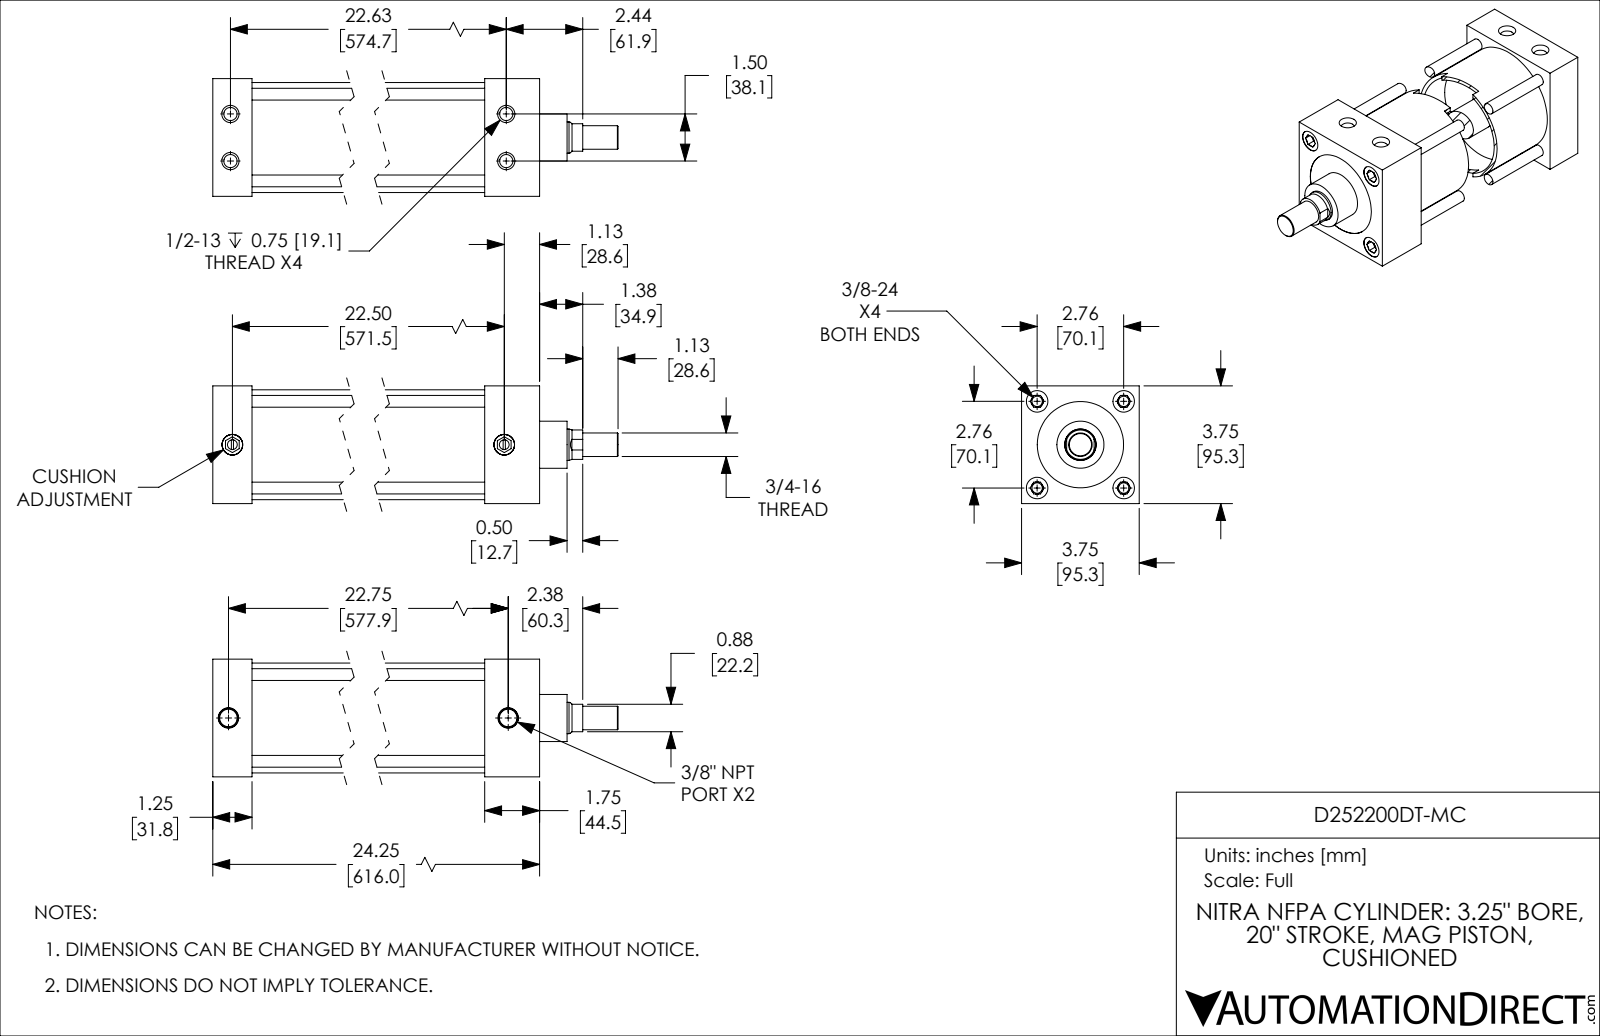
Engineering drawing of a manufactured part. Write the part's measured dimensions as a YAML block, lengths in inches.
part_name: "D252200DT-MC_CUSHION; D252200DT-MC_PISTON_KK1; D252200DT-MC_BODY; D252200DT-MC"
step_written_by: "SolidWorks 2019 (CONFIG_CONTROL_DESIGN)"
units: inches
bodies: {solids: 4, faces: 246, planar: 90, cylindrical: 78, other: 78}
overall_size: [26.75, 3.75, 3.75]
volume: 105.8
surface_area: 787
round_holes:
  - {diameter: 0.332, count: 4}
  - {diameter: 0.422, count: 4}
  - {diameter: 0.687, count: 4}
  - {diameter: 0.312, count: 2}
  - {diameter: 0.562, count: 2}
  - {diameter: 0.656, count: 2}
  - {diameter: 1.001, count: 1}
  - {diameter: 2.75, count: 1}
  - {diameter: 3.251, count: 1}
round_bosses_or_shafts:
  - {diameter: 0.375, count: 4}
  - {diameter: 0.657, count: 2}
  - {diameter: 3.501, count: 1}
  - {diameter: 3.249, count: 1}
  - {diameter: 1.5, count: 1}
  - {diameter: 0.999, count: 1}
  - {diameter: 0.75, count: 1}
partial_cylinders:
  - {radius: 0.469, count: 1}
face_to_face_distances: [1.25, 3.75, 22.5, 21.25, 2.5, 20, 24.25, 23, 21.75, 1.75]
hole_center_spacings: [0.753, 1.952, 2.76, 22.7, 1.5, 3.903, 22.625, 22.674]
